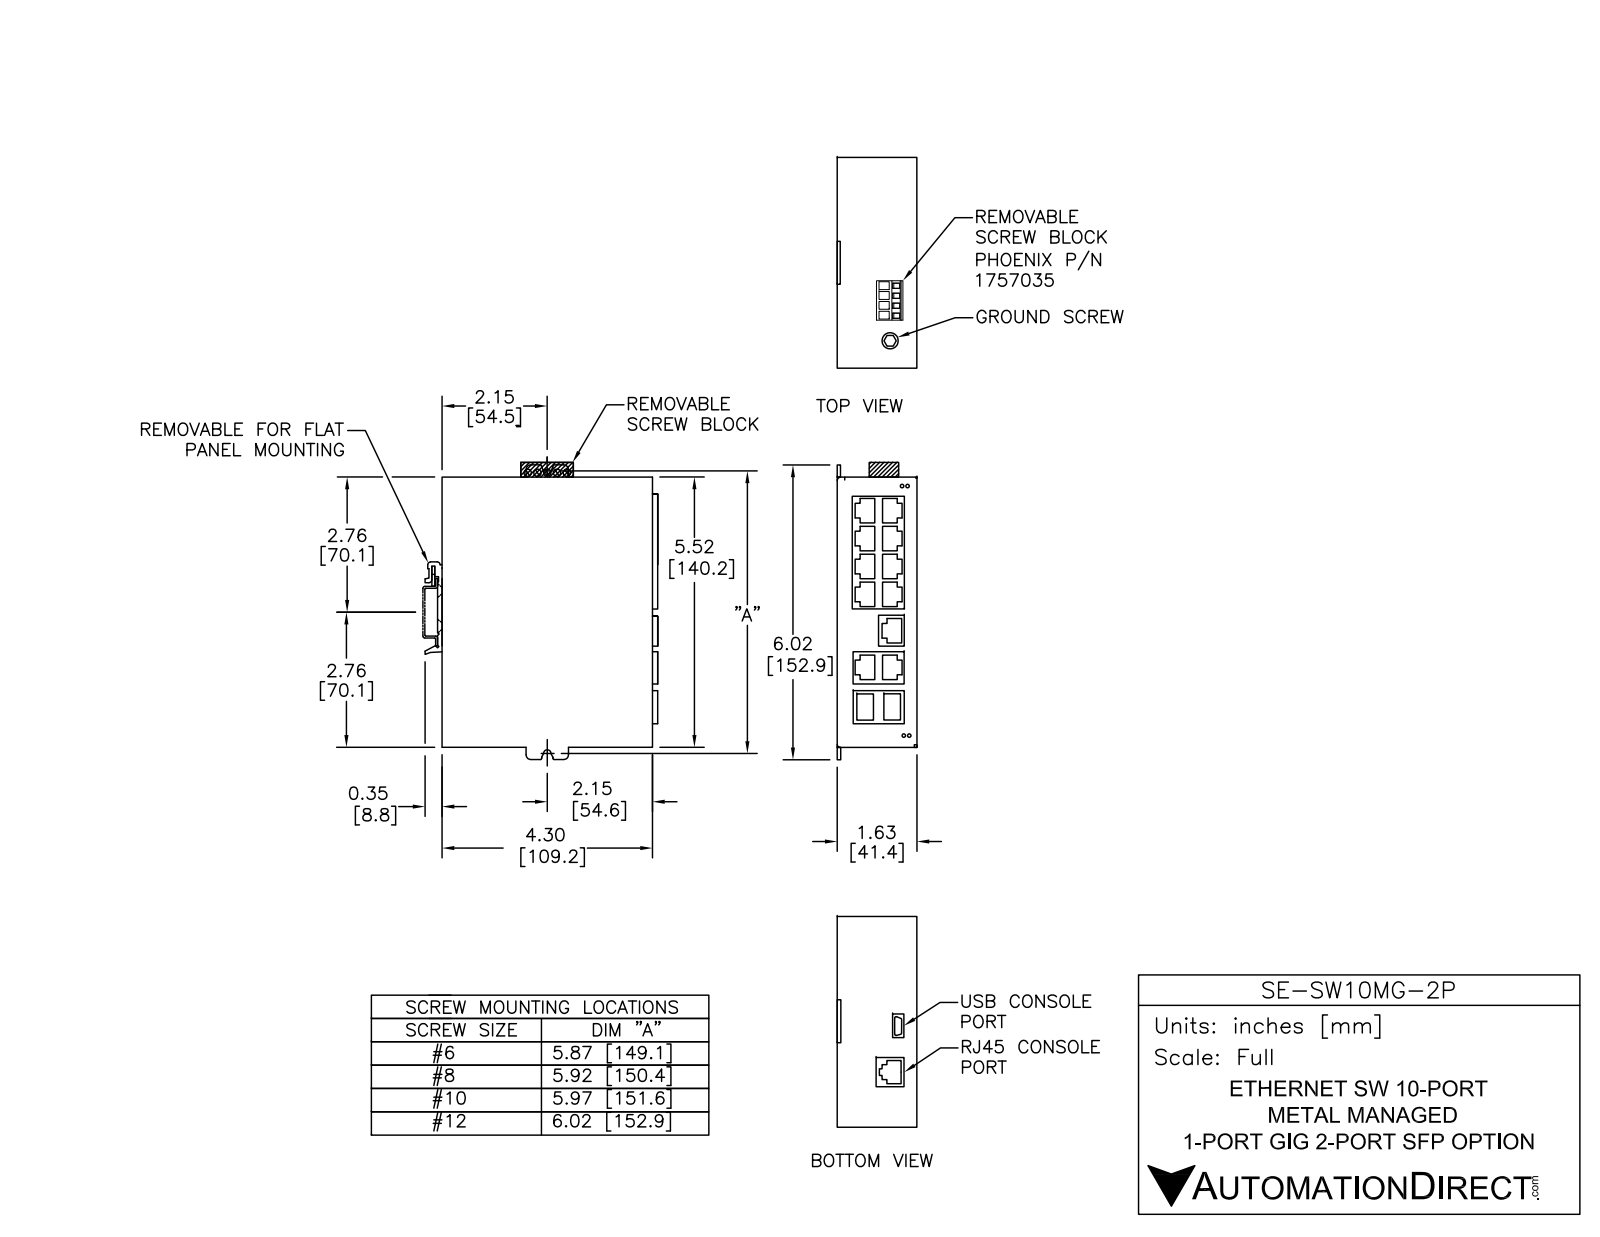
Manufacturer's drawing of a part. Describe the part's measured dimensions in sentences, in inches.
The part is named "SE-SW10MG-2P". Its 3-D file was written by "SolidWorks 2011 (AUTOMOTIVE_DESIGN)". It is 1 solid with 456 faces: 406 planar, 50 cylindrical and 0 other. Overall it measures 6.2 by 4.71 by 1.63 inches. Its volume is 38.55 cubic inches and its surface area 153.6 square inches. Round holes: 4 of diameter 0.11, 4 of diameter 0.138, 1 of diameter 0.239. Round bosses or shafts: 1 of diameter 0.333. Partial cylindrical surfaces (rounded edges, fillets, slot ends): 8 of radius 0.015, 8 of radius 0.1, 6 of radius 0.022, 4 of radius 0.06, 4 of radius 0.07, 2 of radius 0.008, 2 of radius 0.03, 1 of radius 0.077. The main face-to-face distances are 0.06, 0.059, 1.63, 1.57, 1.571, 5.52, 0.09, 4.39, 4.3, 4.241. The hole center spacings are 0.185, 0.37, 5.178, 0.161, 0.168, 0.555, 5.176, 5.184.
